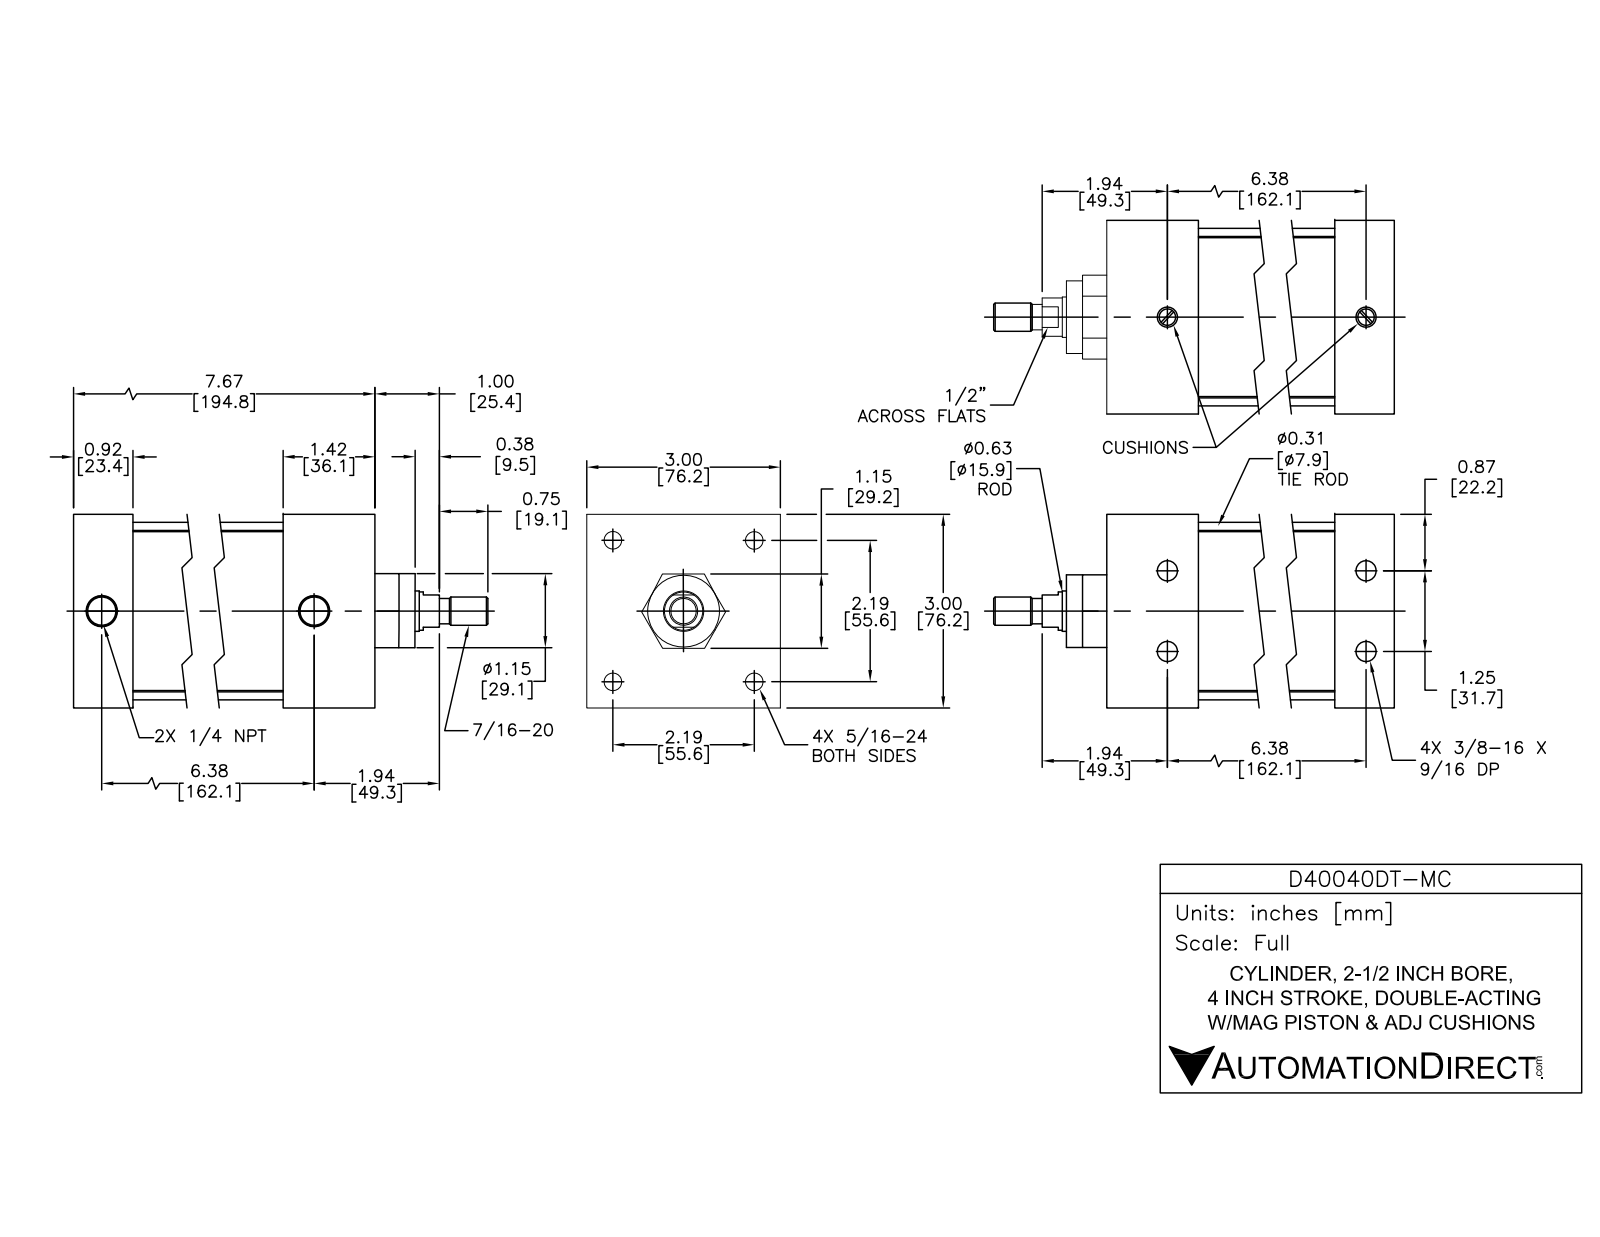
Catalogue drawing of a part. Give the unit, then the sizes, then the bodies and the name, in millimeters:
Units: millimetres
Overall size (bounding box): 241.2 × 76.2 × 76.2
Round holes (diameter × count): ⌀6.8 ×4, ⌀7.8 ×4, ⌀9.1 ×4, ⌀12.7 ×4, ⌀7.5 ×2, ⌀12.1 ×2, ⌀15.9 ×1, ⌀16 ×1, ⌀63.5 ×1
Round bosses / shafts (diameter × count): ⌀12.3 ×4, ⌀8 ×4, ⌀7.2 ×4, ⌀69.9 ×1, ⌀63.4 ×1, ⌀28.4 ×1, ⌀15.8 ×1, ⌀15 ×1
Partial cylindrical surfaces — rounded edges, fillets, slot ends (radius × count): R7.6 ×4
Main face-to-face distances: 76.2, 2, 135.3, 196.7, 170.8, 25.9, 36.1, 134.8, 160.7, 25.4
Hole centre spacings: 39.5, 55.9, 162.6, 161.8, 15.9, 15.9, 31.8, 79
Volume: 582 600 mm³ · Surface area: 155 200 mm²
Bodies: 12 solids, 298 faces (94 planar, 114 cylindrical, 90 other)
Part name (STEP PRODUCT): D40040DT-M BODY; D40040DT-MC; D40040DT-M PISTON
STEP written by: SolidWorks 2015 (AUTOMOTIVE_DESIGN)
